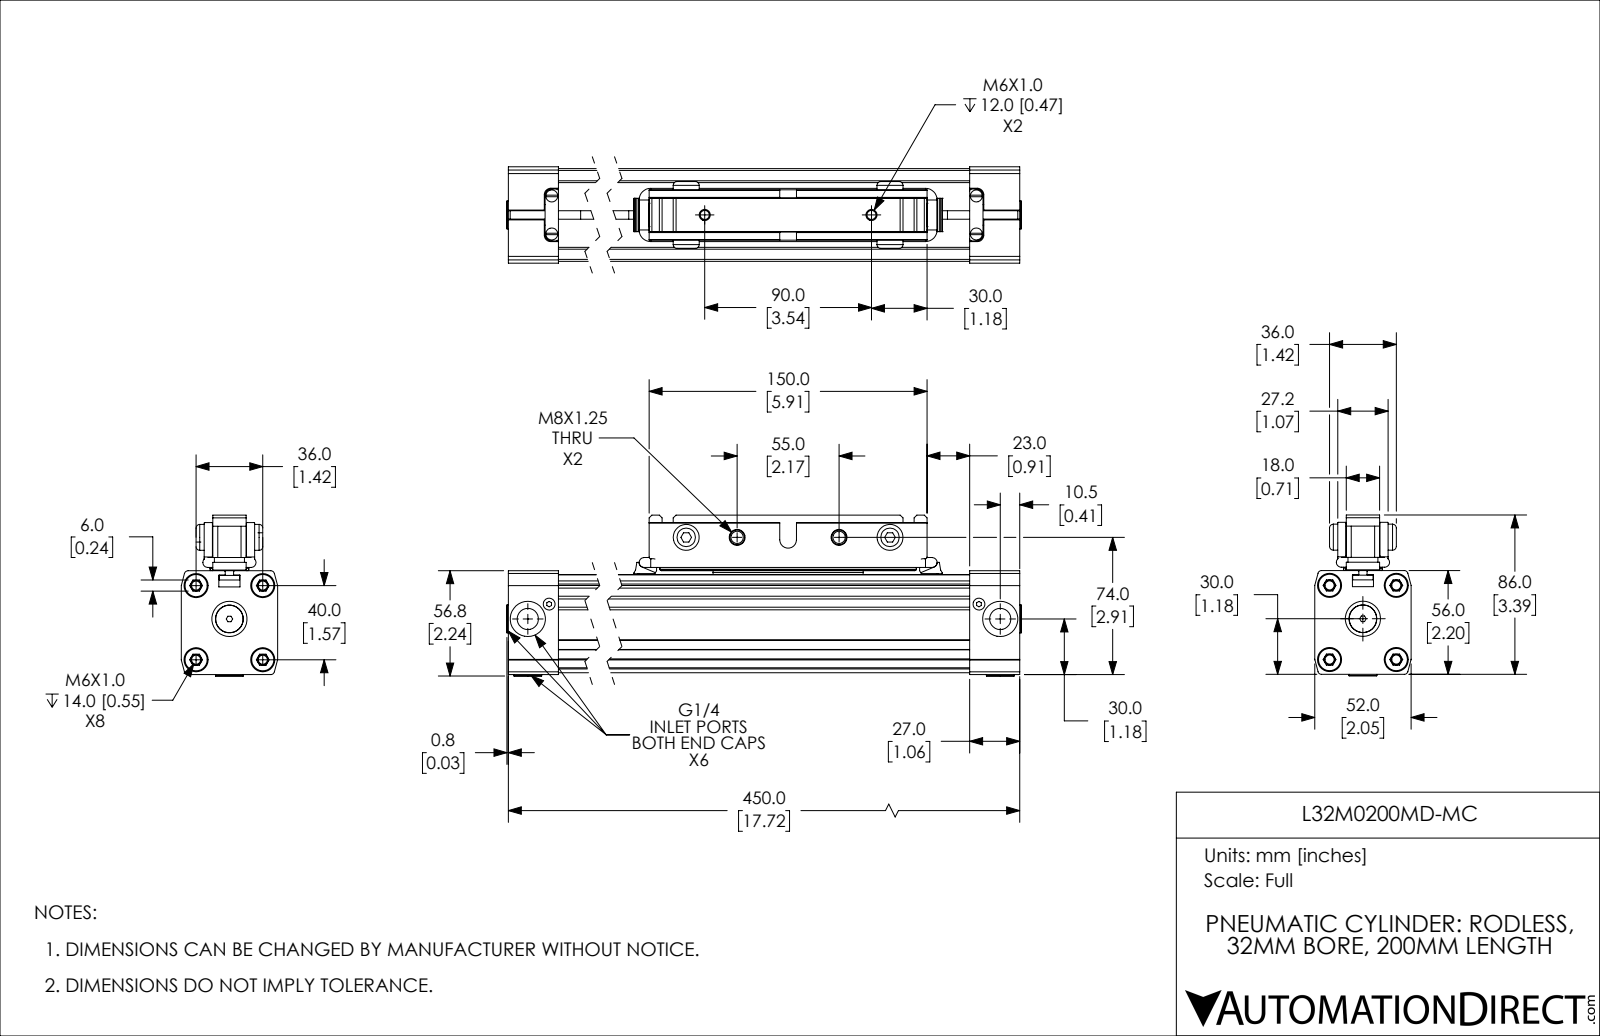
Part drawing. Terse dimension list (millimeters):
name: L32M0200MD-MC_BODY; L32M0200MD-MC_PISTON; L32M0200MD-MC
written by: SolidWorks 2019 (CONFIG_CONTROL_DESIGN)
unit: mm
bodies: 13 solids, 822 faces (433 planar, 273 cylindrical, 116 other)
size: 451.6 × 86.8 × 52
volume: 988 500 mm³; area: 247 700 mm²
holes: 6× ⌀4.9, 5× ⌀11.5, 5× ⌀19, 4× ⌀6.5, 4× ⌀6.7, 4× ⌀8.6, 4× ⌀13, 2× ⌀6.4, 1× ⌀32.1
bosses: 4× ⌀12, 4× ⌀5.3, 3× ⌀15, 3× ⌀9.7, 3× ⌀8.2, 2× ⌀14, 1× ⌀32, 1× ⌀31.8
rounds: 22× R1, 18× R2, 8× R3.5, 4× R0.3, 4× R0.5, 4× R0.6, 4× R4, 2× R0.2
face distances: 53, 50, 11.3, 5.1, 4.6, 14, 11.4, 38.6, 1, 6.1
hole spacings: 16.5, 416.2, 14, 20.5, 23.7, 25.5, 27.5, 28.4
